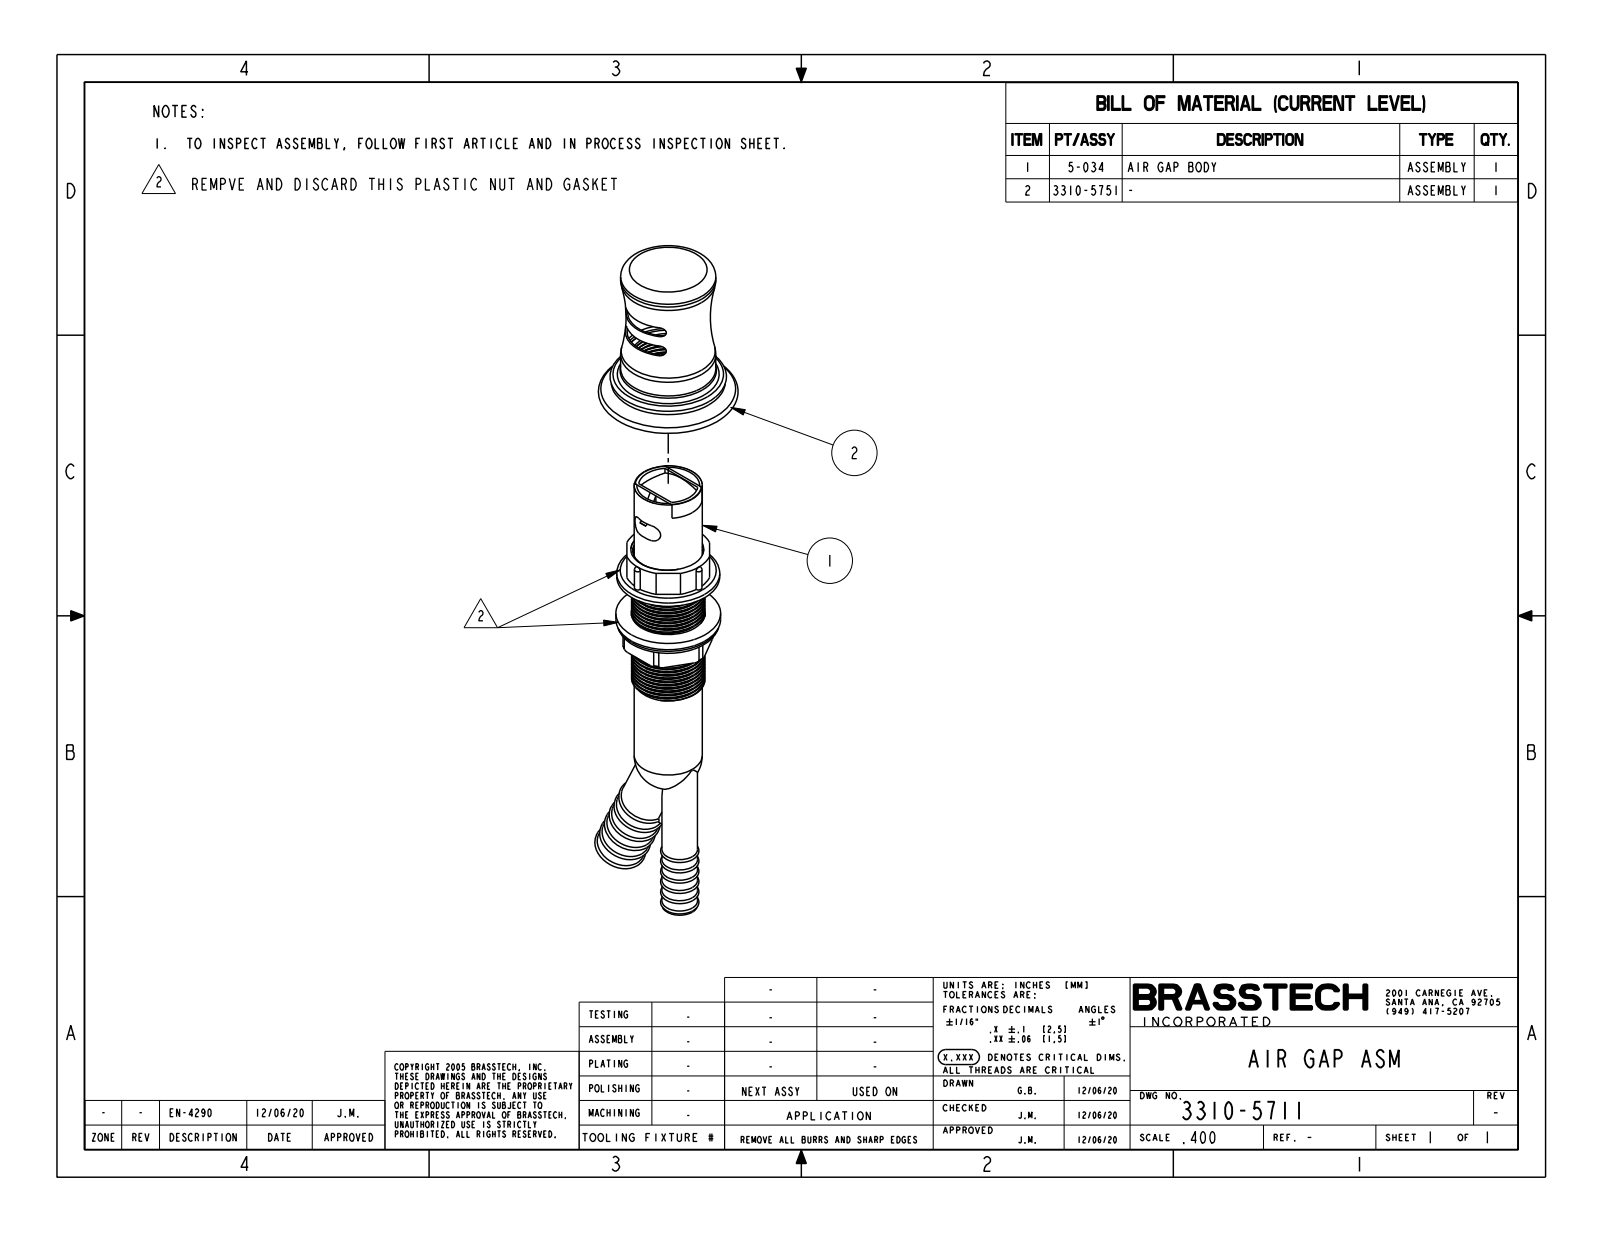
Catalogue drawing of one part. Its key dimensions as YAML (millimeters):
part_name: "3310-5711"
step_written_by: "CREO PARAMETRIC BY PTC INC, 2018400 (CONFIG_CONTROL_DESIGN)"
units: millimeters
bodies: {solids: 1, faces: 60, planar: 27, cylindrical: 8, other: 25}
overall_size: [66.7, 61, 61]
volume: 92750
surface_area: 13790
round_bosses_or_shafts:
  - {diameter: 41.5, count: 1}
partial_cylinders:
  - {radius: 2.5, count: 4}
face_to_face_distances: [66.7, 10.8, 55.9, 5, 27.9, 10, 33.8, 23, 32.9, 48.7]
